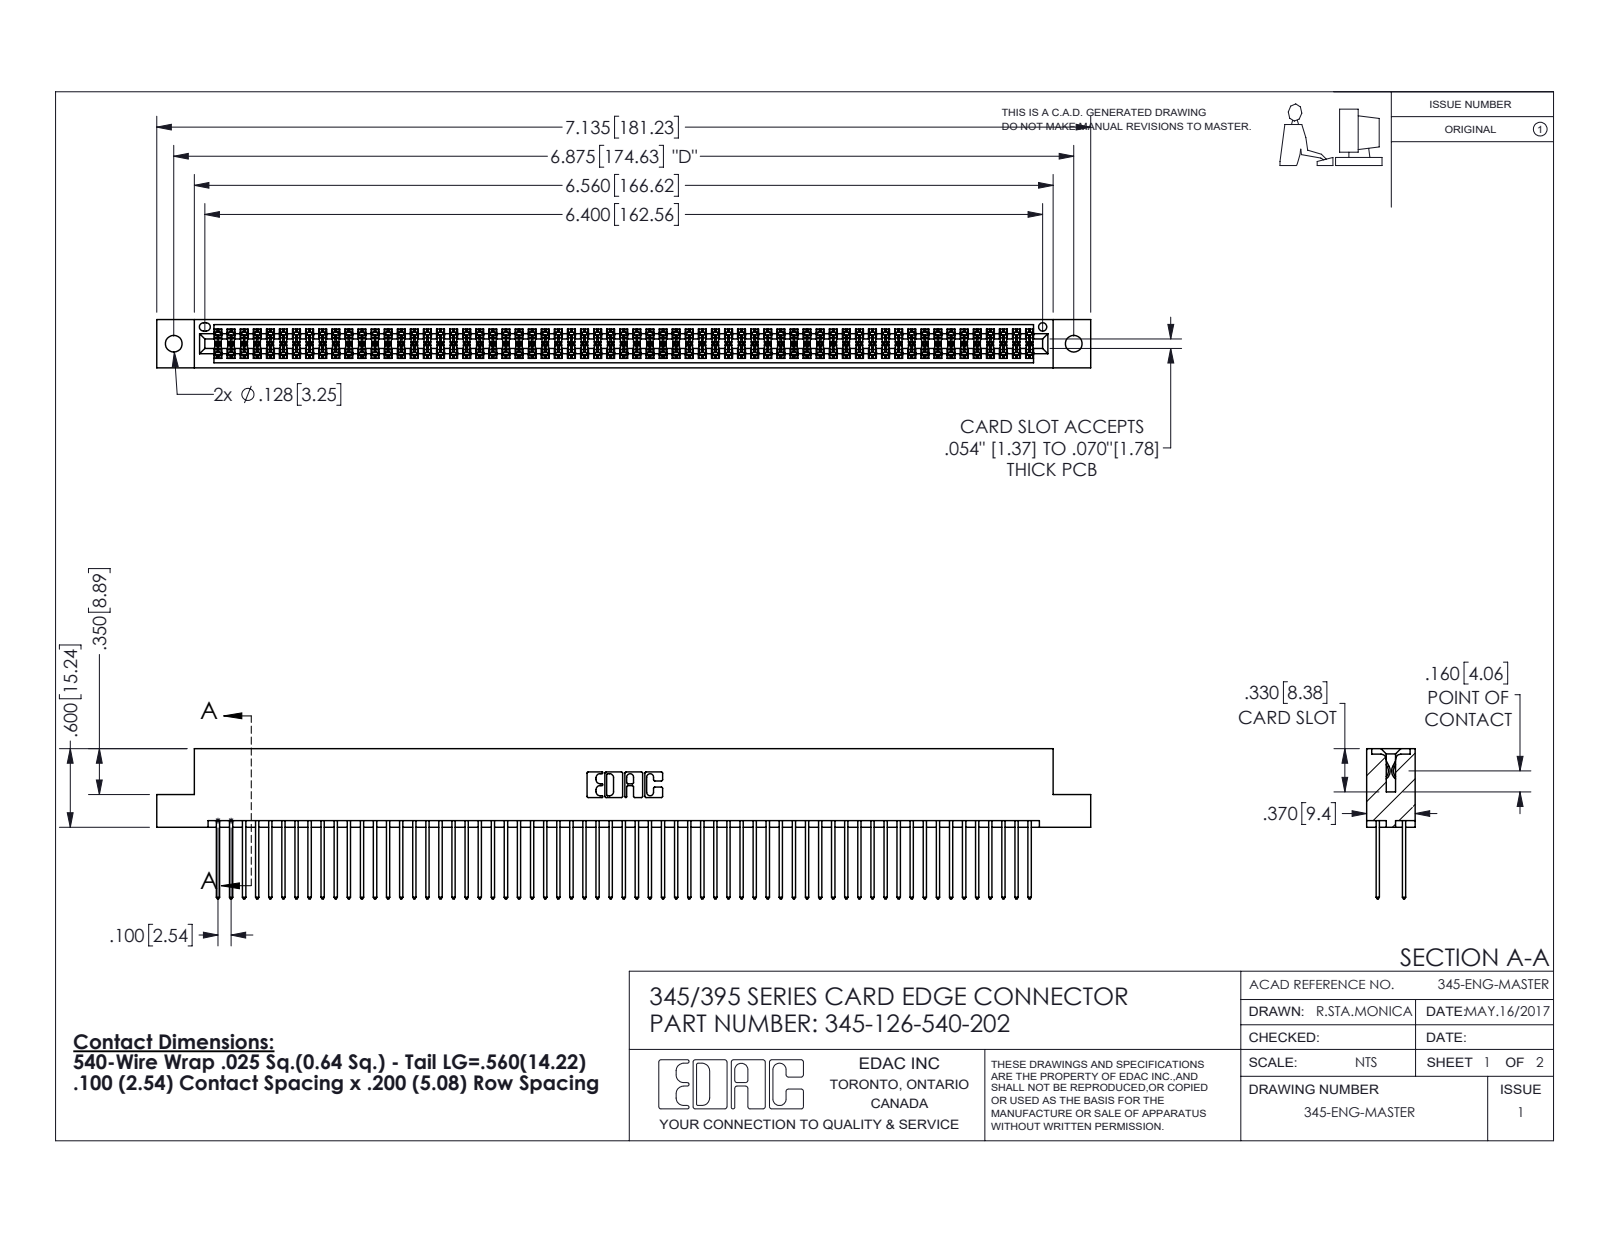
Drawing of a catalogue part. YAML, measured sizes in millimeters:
part_name: "345-292-001_345-293-140; 345-126-540-202; 345 Part_Flush Mounting Lugs - 0.128 Dia"
step_written_by: "SolidWorks 2016 (CONFIG_CONTROL_DESIGN)"
units: millimeters
bodies: {solids: 127, faces: 6426, planar: 4238, cylindrical: 2188, other: 0}
overall_size: [181.2, 29.1, 9.4]
volume: 18240
surface_area: 29320
round_holes:
  - {diameter: 3.3, count: 2}
  - {diameter: 1.6, count: 1}
partial_cylinders:
  - {radius: 0.2, count: 189}
  - {radius: 0.3, count: 126}
  - {radius: 0.3, count: 22}
  - {radius: 0.2, count: 6}
  - {radius: 0.8, count: 6}
  - {radius: 0.7, count: 3}
  - {radius: 0.4, count: 2}
  - {radius: 0.5, count: 2}
face_to_face_distances: [7.6, 1.8, 5.1, 2.5, 6.9, 0.6, 9.4, 5.7, 4.4, 3.8]
hole_center_spacings: [6.9, 168.6, 174.6]
